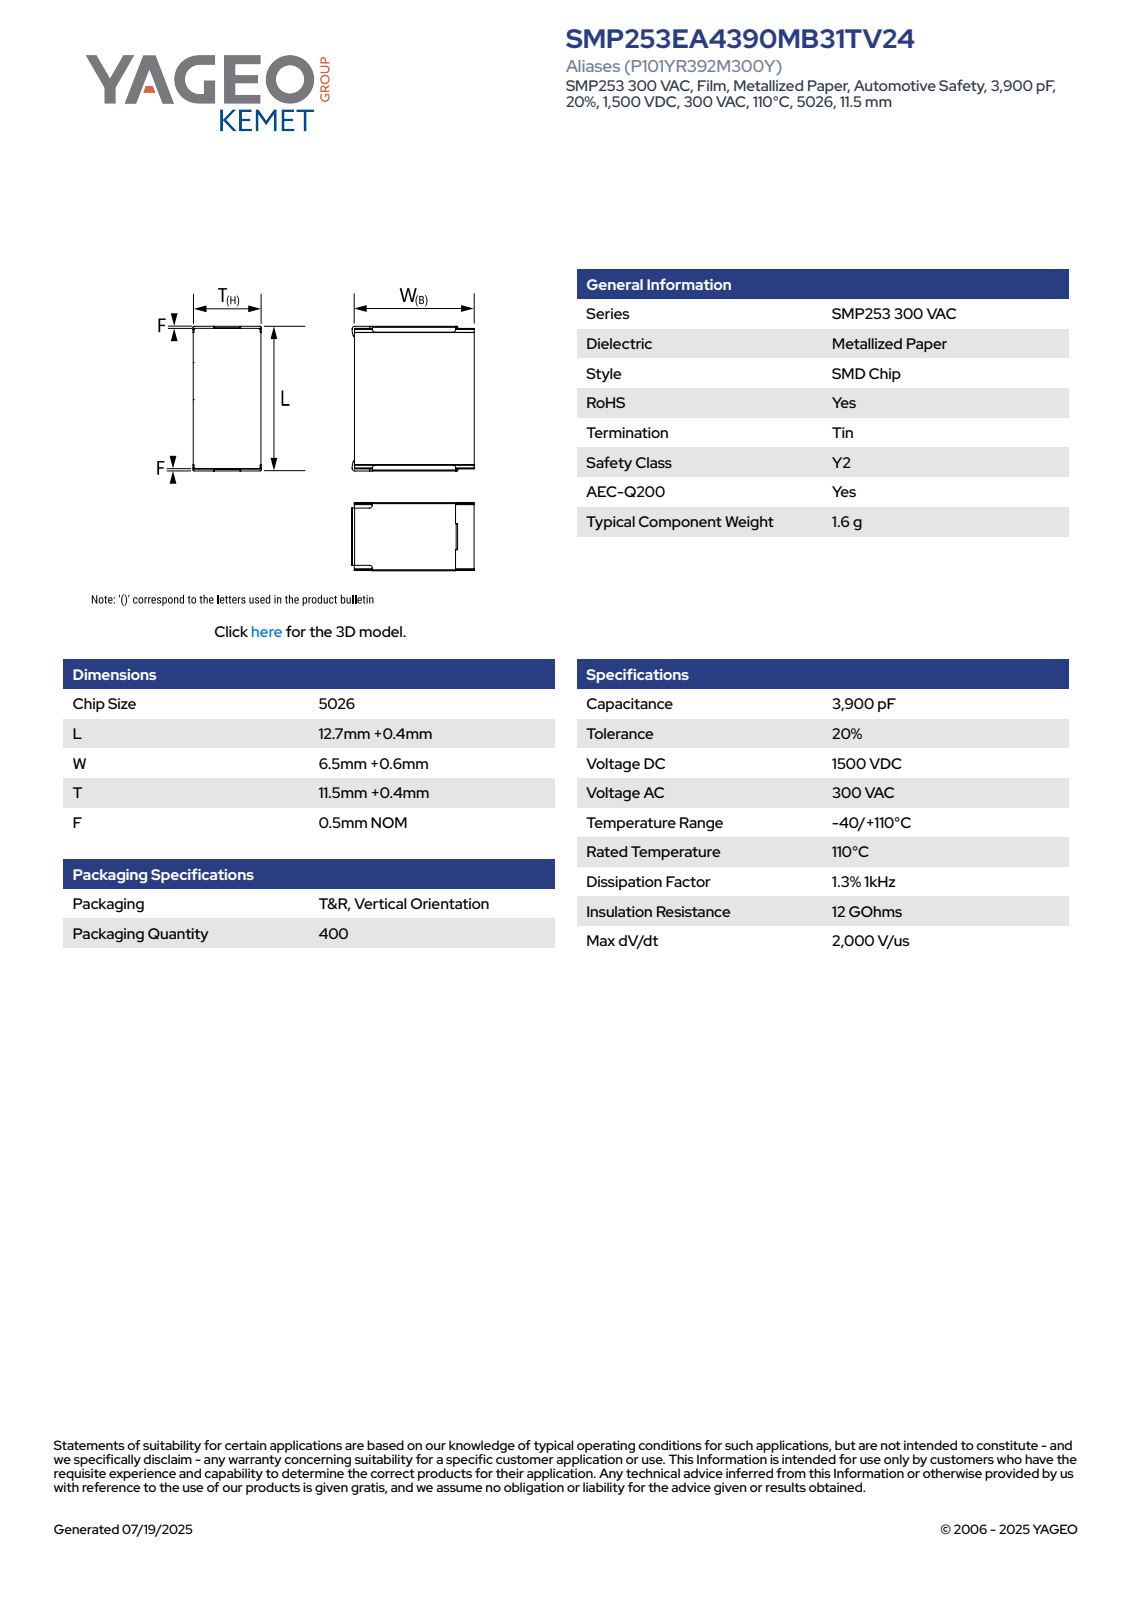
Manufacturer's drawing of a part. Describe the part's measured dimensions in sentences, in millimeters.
The part is named "CFS_KSTD_5026_L13.1W7.1T11.9F0.5". Its 3-D file was written by "SolidWorks 2021 (AUTOMOTIVE_DESIGN)". It is 4 solids with 117 faces: 103 planar, 14 cylindrical and 0 other. Overall it measures 13.1 by 12.51 by 7.34 millimeters. Its volume is 1 062 cubic millimeters and its surface area 687 square millimeters. Partial cylindrical surfaces (rounded edges, fillets, slot ends): 10 of radius 0.71, 4 of radius 0.46. The main face-to-face distances are 6.82, 11.9, 0.5, 12.6, 13.1, 12.1, 12.2, 7.34, 0.52, 7.1.
